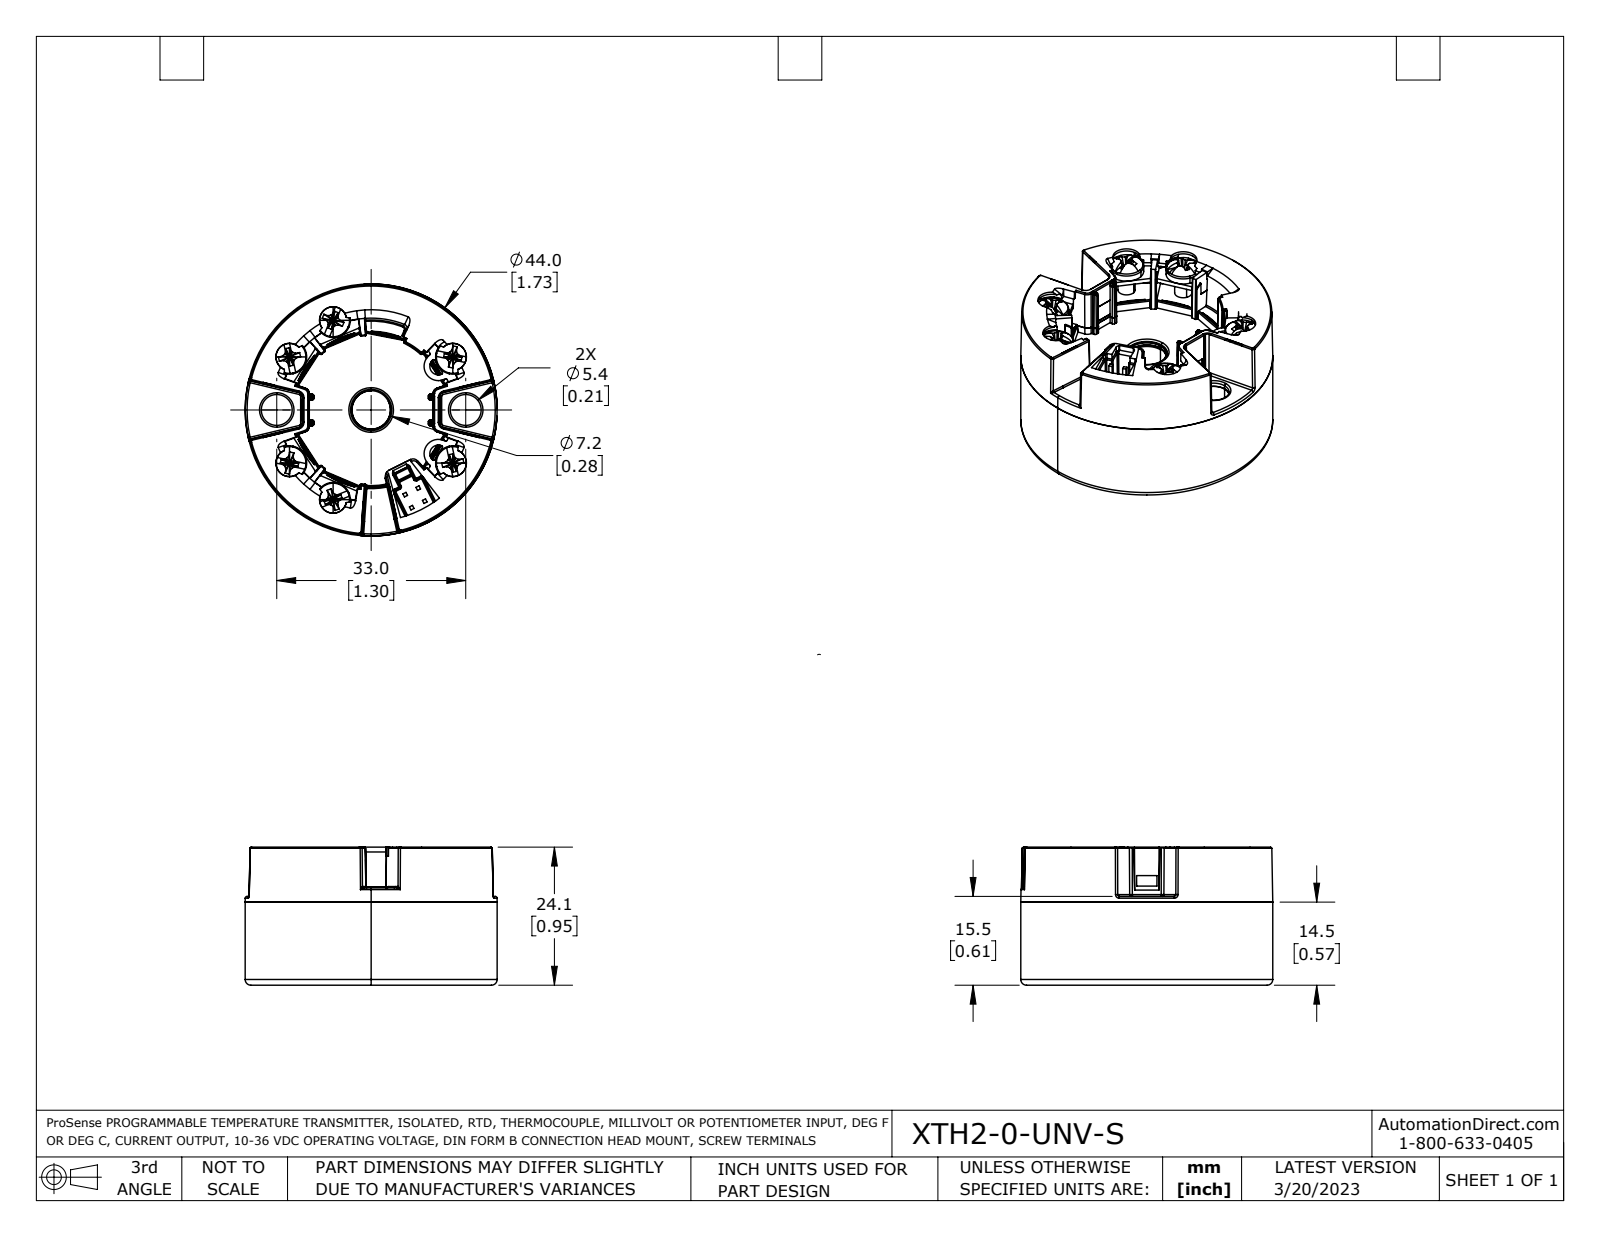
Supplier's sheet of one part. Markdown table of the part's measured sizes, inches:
| quantity | value |
| --- | --- |
| part name | OTMT71-LFA1AAAA1AD+B2C1 Ext1b nc b2drftCc fxtr1Cb fxt r1 sr1 n1 TOPonly fxtr1 wbevcut compl 1C fxt sr1 |
| STEP written by | SolidWorks 2021 (AUTOMOTIVE_DESIGN) |
| units | inches |
| bodies | 2 solids, 1317 faces (492 planar, 294 cylindrical, 531 other) |
| overall size | 1.732 × 1.732 × 0.949 |
| volume | 1.658 in³ |
| surface area | 20.92 in² |
| round holes (diameter × count) | 0.126 × 6, 0.212 × 2, 0.094 × 1, 0.213 × 1, 0.264 × 1, 0.283 × 1 |
| round bosses / shafts (diameter × count) | 0.118 × 6, 0.265 × 1 |
| partial cylindrical surfaces (radius × count) | 0.008 × 80, 0.039 × 16, 0.012 × 15, 0.118 × 6, 0.12 × 5, 0.009 × 4, 0.012 × 3, 0.013 × 3 |
| main face-to-face distances | 0.571, 0.039, 0.61, 0.339, 0.949, 0.378, 0.059, 0.28, 0.098, 0.669 |
| hole center spacings | 0.669, 0.375, 0.375, 0.391, 0.65, 0.67, 0.728, 0.729 |
